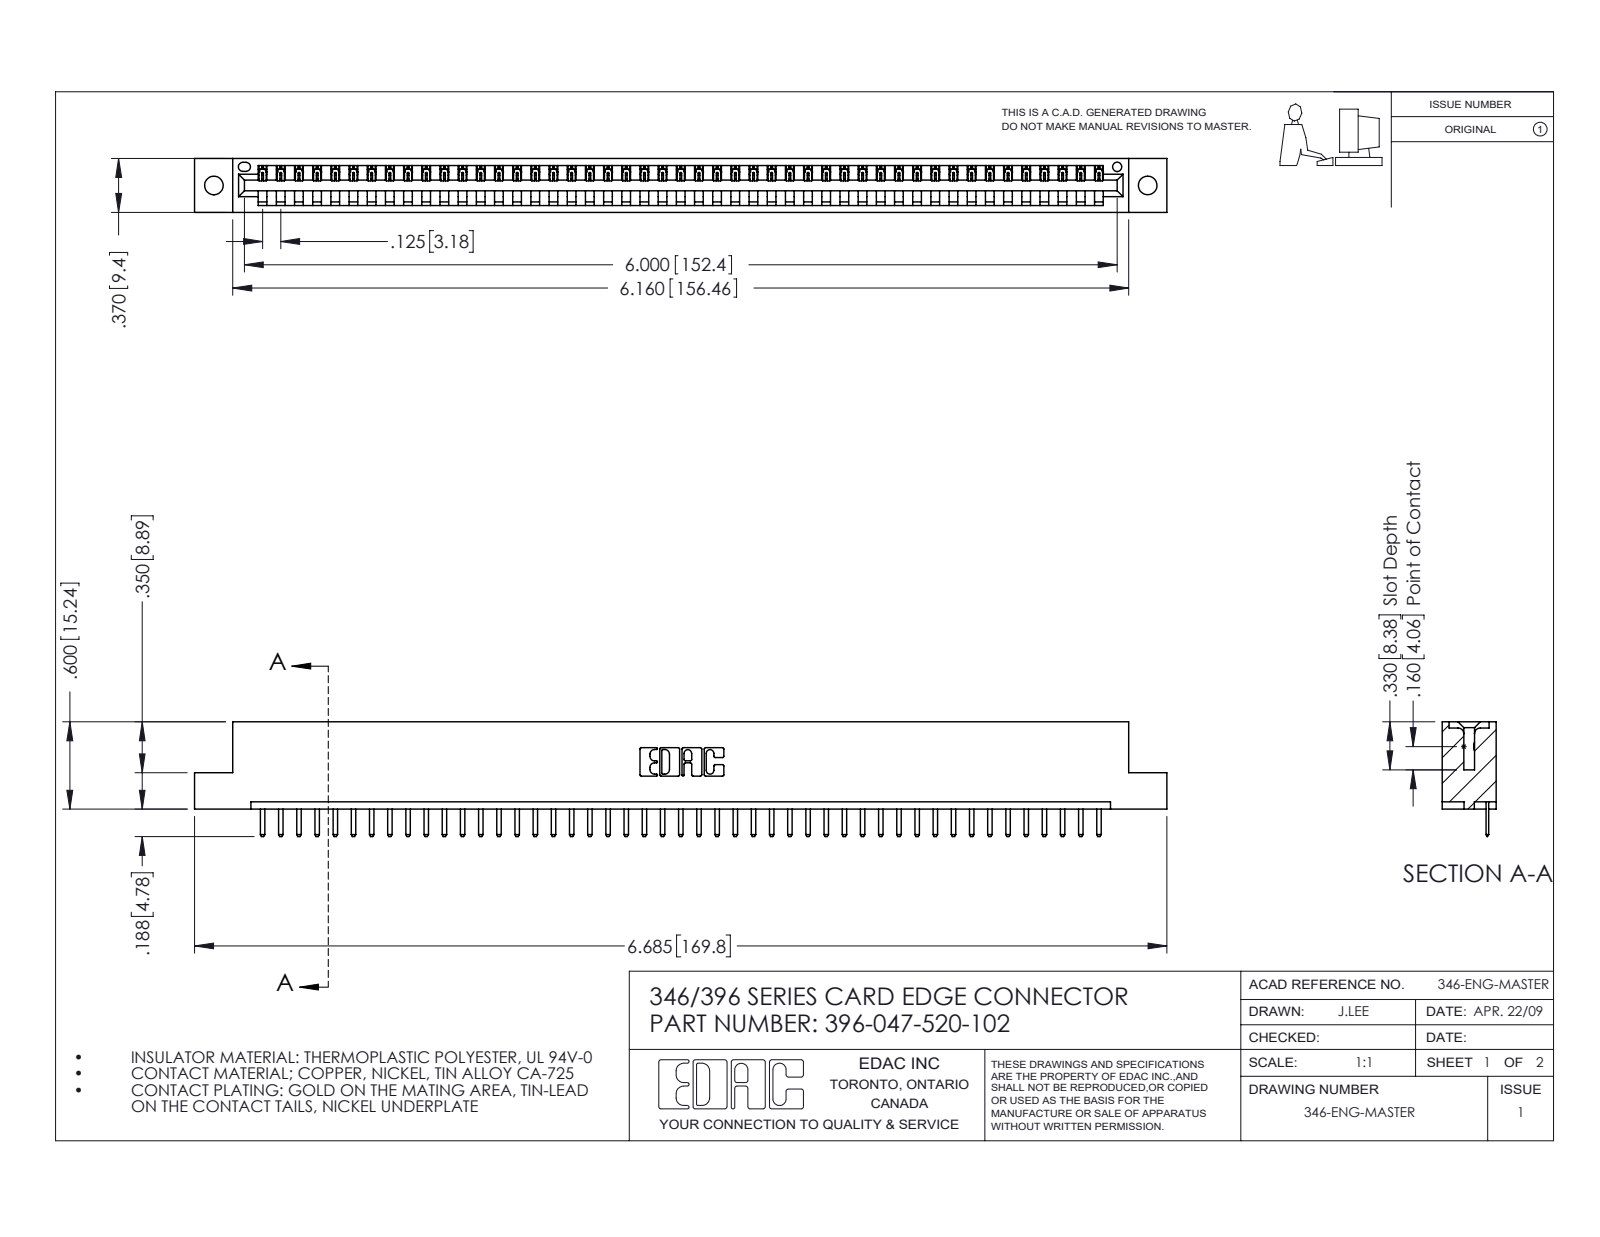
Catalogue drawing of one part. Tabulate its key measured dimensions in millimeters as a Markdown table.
| quantity | value |
| --- | --- |
| part name | 396-047-520-102; 346 Part_Flush Mounting Lugs - 0.128 Dia; 345-292-001_345-293-120 |
| STEP written by | SolidWorks 2016 (CONFIG_CONTROL_DESIGN) |
| units | millimeters |
| bodies | 48 solids, 3036 faces (2050 planar, 986 cylindrical, 0 other) |
| overall size | 169.8 × 20 × 9.4 |
| volume | 16 100 mm³ |
| surface area | 19 480 mm² |
| round holes (diameter × count) | 3.3 × 2, 1.6 × 1 |
| partial cylindrical surfaces (radius × count) | 0.3 × 96, 0.2 × 94, 0.3 × 22, 0.2 × 6, 0.8 × 6, 0.7 × 3, 0.8 × 2, 1 × 2 |
| main face-to-face distances | 1.2, 8.2, 9.4, 6.4, 3.8, 5.6, 2.5, 4.4, 1.8, 7.6 |
| hole center spacings | 6.2, 157.8, 163.1 |
